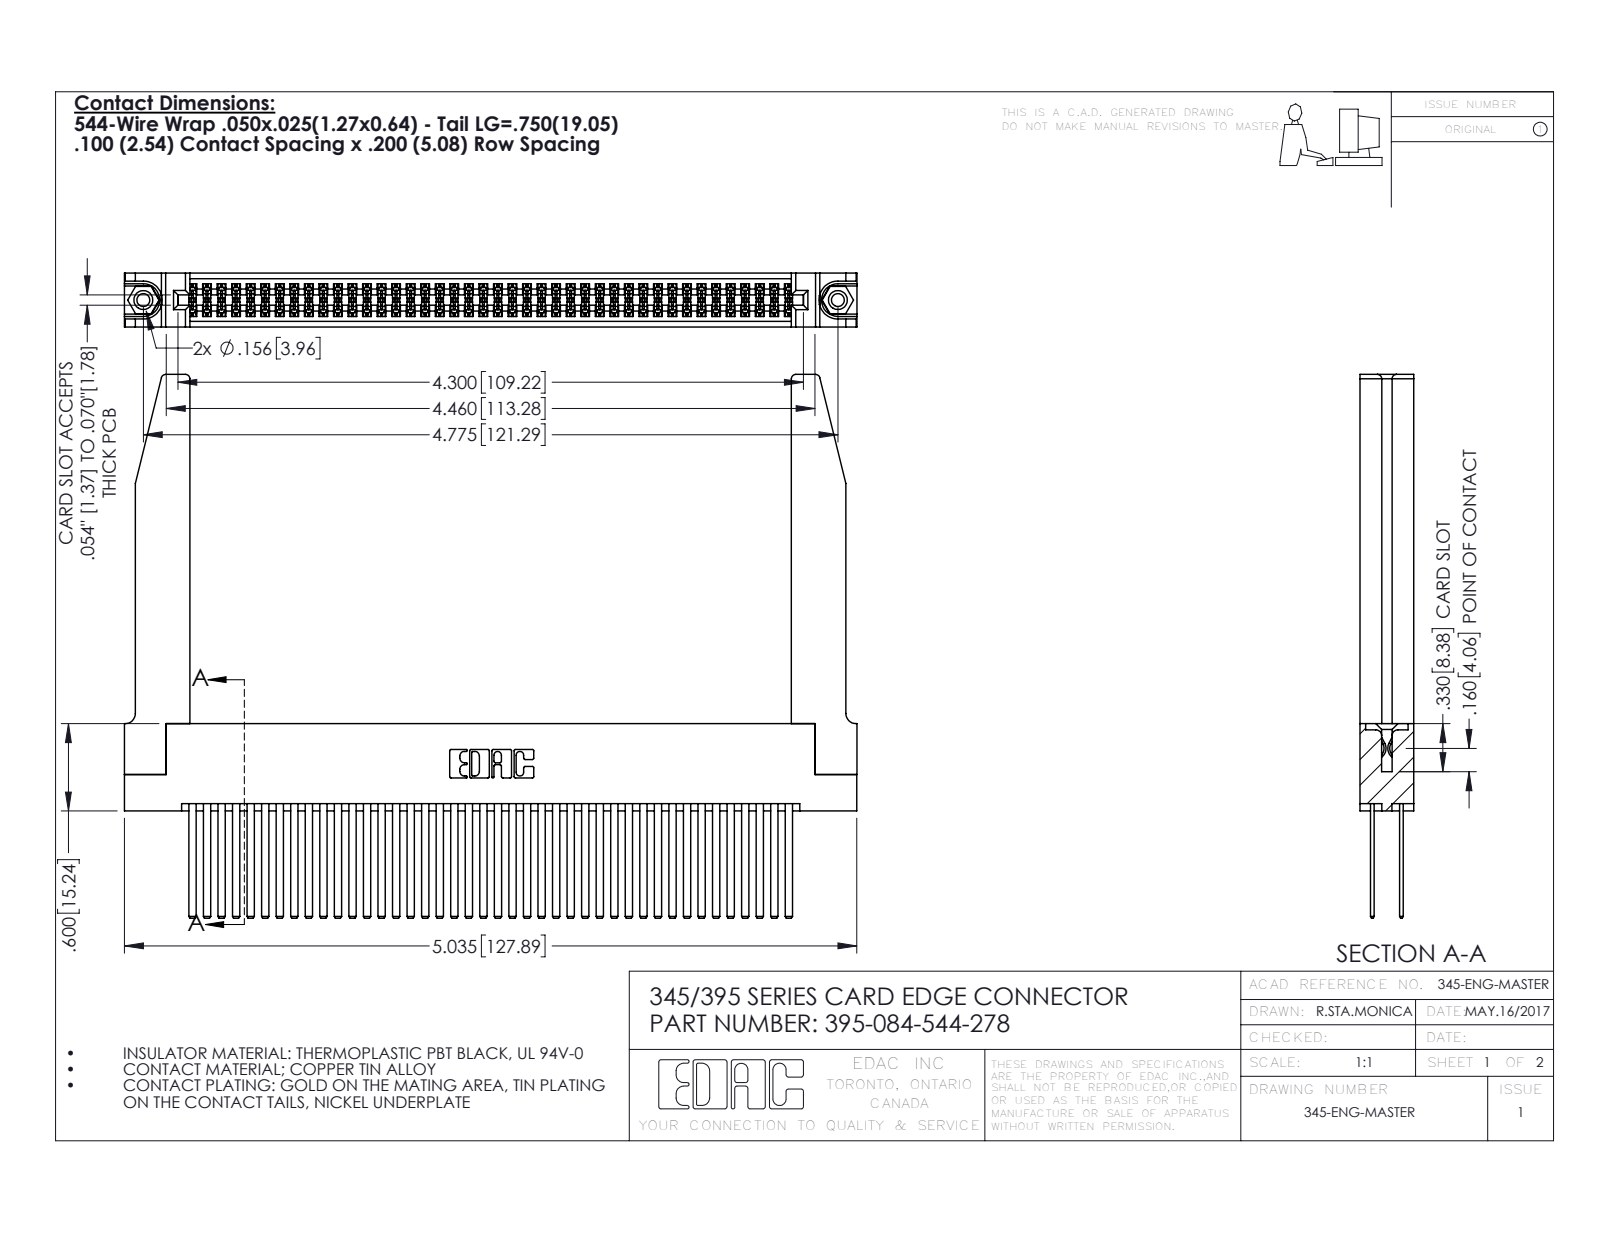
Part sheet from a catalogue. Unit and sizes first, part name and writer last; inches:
Units: inches
Overall size (bounding box): 5.036 × 3.737 × 0.37
Round holes (diameter × count): ⌀0.089 ×2, ⌀0.125 ×2, ⌀0.156 ×2, ⌀0.064 ×1
Round bosses / shafts (diameter × count): ⌀0.155 ×2
Partial cylindrical surfaces — rounded edges, fillets, slot ends (radius × count): R0.006 ×126, R0.01 ×22, R0.03 ×8, R0.007 ×6, R0.031 ×6, R0.026 ×3, R0.014 ×2, R0.019 ×2
Main face-to-face distances: 0.072, 0.298, 0.2, 0.098, 0.272, 0.025, 0.37, 0.225, 0.175, 0.148
Hole centre spacings: 0.27, 4.539, 4.775
Volume: 1.304 in³ · Surface area: 47.12 in²
Bodies: 89 solids, 4056 faces (2658 planar, 1346 cylindrical, 52 other)
Part name (STEP PRODUCT): 345-250-001_345-250-001-102; 395-084-544-278; 345-220-078_345-220-078; 345-292-001_345-293-144 (+1 more)
STEP written by: SolidWorks 2016 (CONFIG_CONTROL_DESIGN)
